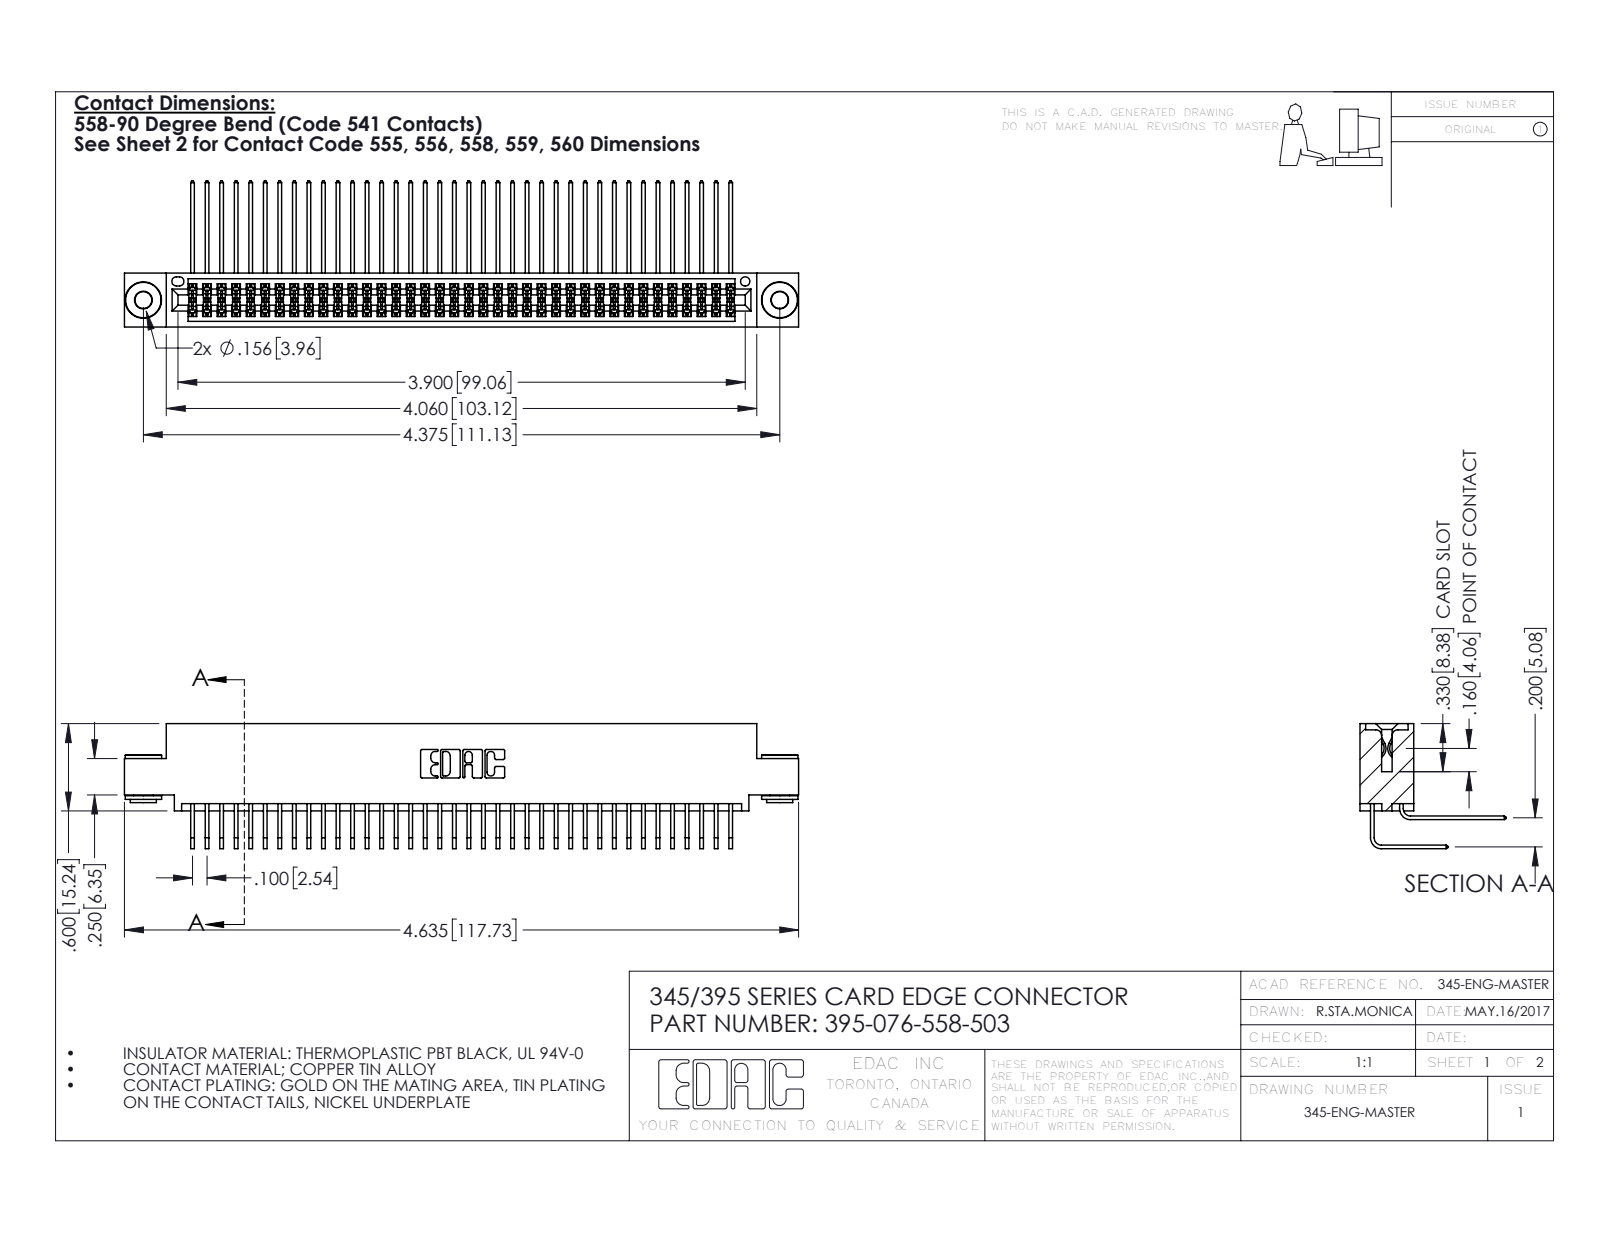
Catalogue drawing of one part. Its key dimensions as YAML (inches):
part_name: "345-292-001_558 Tail - 2; 345-250-002_345-250-002-102; 345-292-001_558 559 Tail - 1; 345 Part_0.110 Offset - 0.156 Dia-TH (+1 more)"
step_written_by: "SolidWorks 2016 (CONFIG_CONTROL_DESIGN)"
units: inches
bodies: {solids: 79, faces: 4120, planar: 2754, cylindrical: 1358, other: 8}
overall_size: [4.635, 1.005, 0.859]
volume: 0.719
surface_area: 30.54
round_holes:
  - {diameter: 0.116, count: 2}
  - {diameter: 0.156, count: 2}
  - {diameter: 0.064, count: 1}
round_bosses_or_shafts:
  - {diameter: 0.25, count: 2}
  - {diameter: 0.18, count: 2}
  - {diameter: 0.136, count: 2}
partial_cylinders:
  - {radius: 0.006, count: 115}
  - {radius: 0.01, count: 22}
  - {radius: 0.007, count: 6}
  - {radius: 0.031, count: 6}
  - {radius: 0.026, count: 3}
  - {radius: 0.014, count: 2}
  - {radius: 0.019, count: 2}
  - {radius: 0.022, count: 2}
face_to_face_distances: [0.072, 0.298, 0.2, 0.37, 0.025, 0.098, 0.272, 0.225, 0.025, 0.175]
hole_center_spacings: [0.27, 4.139, 4.375]
